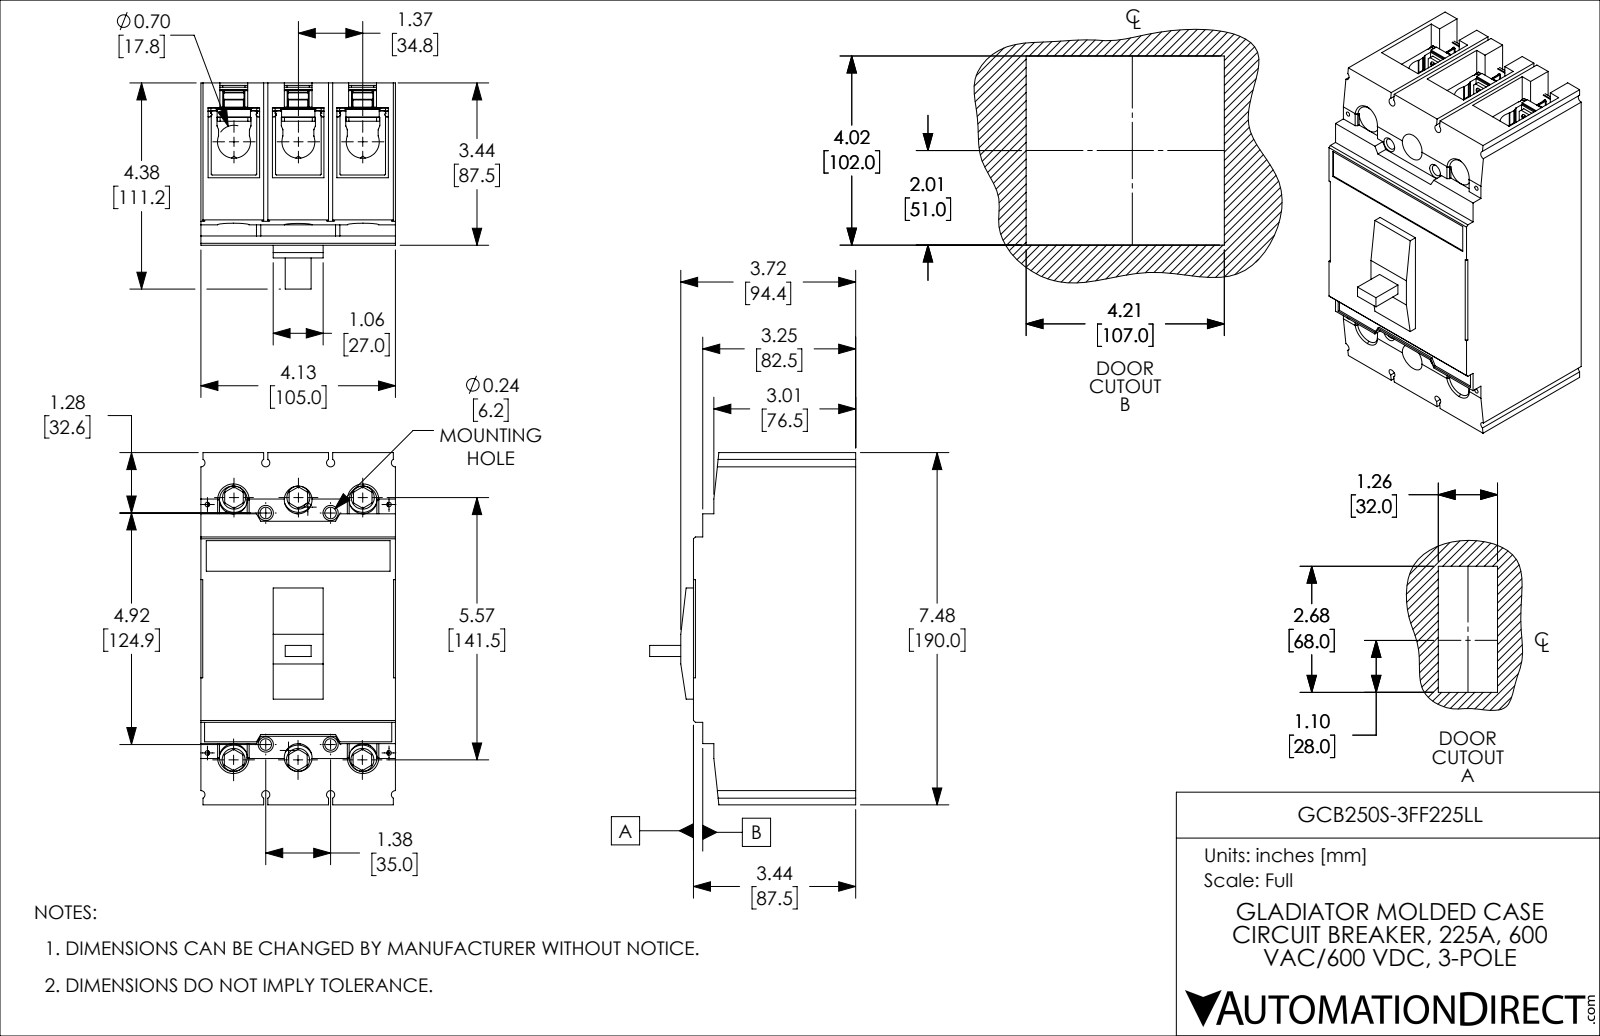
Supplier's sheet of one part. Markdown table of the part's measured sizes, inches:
| quantity | value |
| --- | --- |
| part name | GCB250S-3FF225LL |
| STEP written by | SolidWorks 2021 (CONFIG_CONTROL_DESIGN) |
| units | inches |
| bodies | 25 solids, 2233 faces (975 planar, 958 cylindrical, 300 other) |
| overall size | 7.48 × 4.378 × 4.134 |
| volume | 87.11 in³ |
| surface area | 315.7 in² |
| round holes (diameter × count) | 0.067 × 24, 0.157 × 24, 0.098 × 10, 0.354 × 6, 0.591 × 6, 0.689 × 6, 0.173 × 4, 0.244 × 4 |
| round bosses / shafts (diameter × count) | 0.709 × 6 |
| partial cylindrical surfaces (radius × count) | 0.012 × 206, 0.039 × 72, 0.059 × 36, 0.02 × 26, 0.008 × 24, 0.079 × 20, 0.016 × 12, 0.031 × 12 |
| main face-to-face distances | 1.368, 4.134, 2.736, 1.094, 0.843, 0.252, 0.059, 1.378, 6.102, 3.445 |
| hole center spacings | 0.285, 0.743, 1.046, 1.378, 5.24, 6.298, 1.368, 1.426 |
